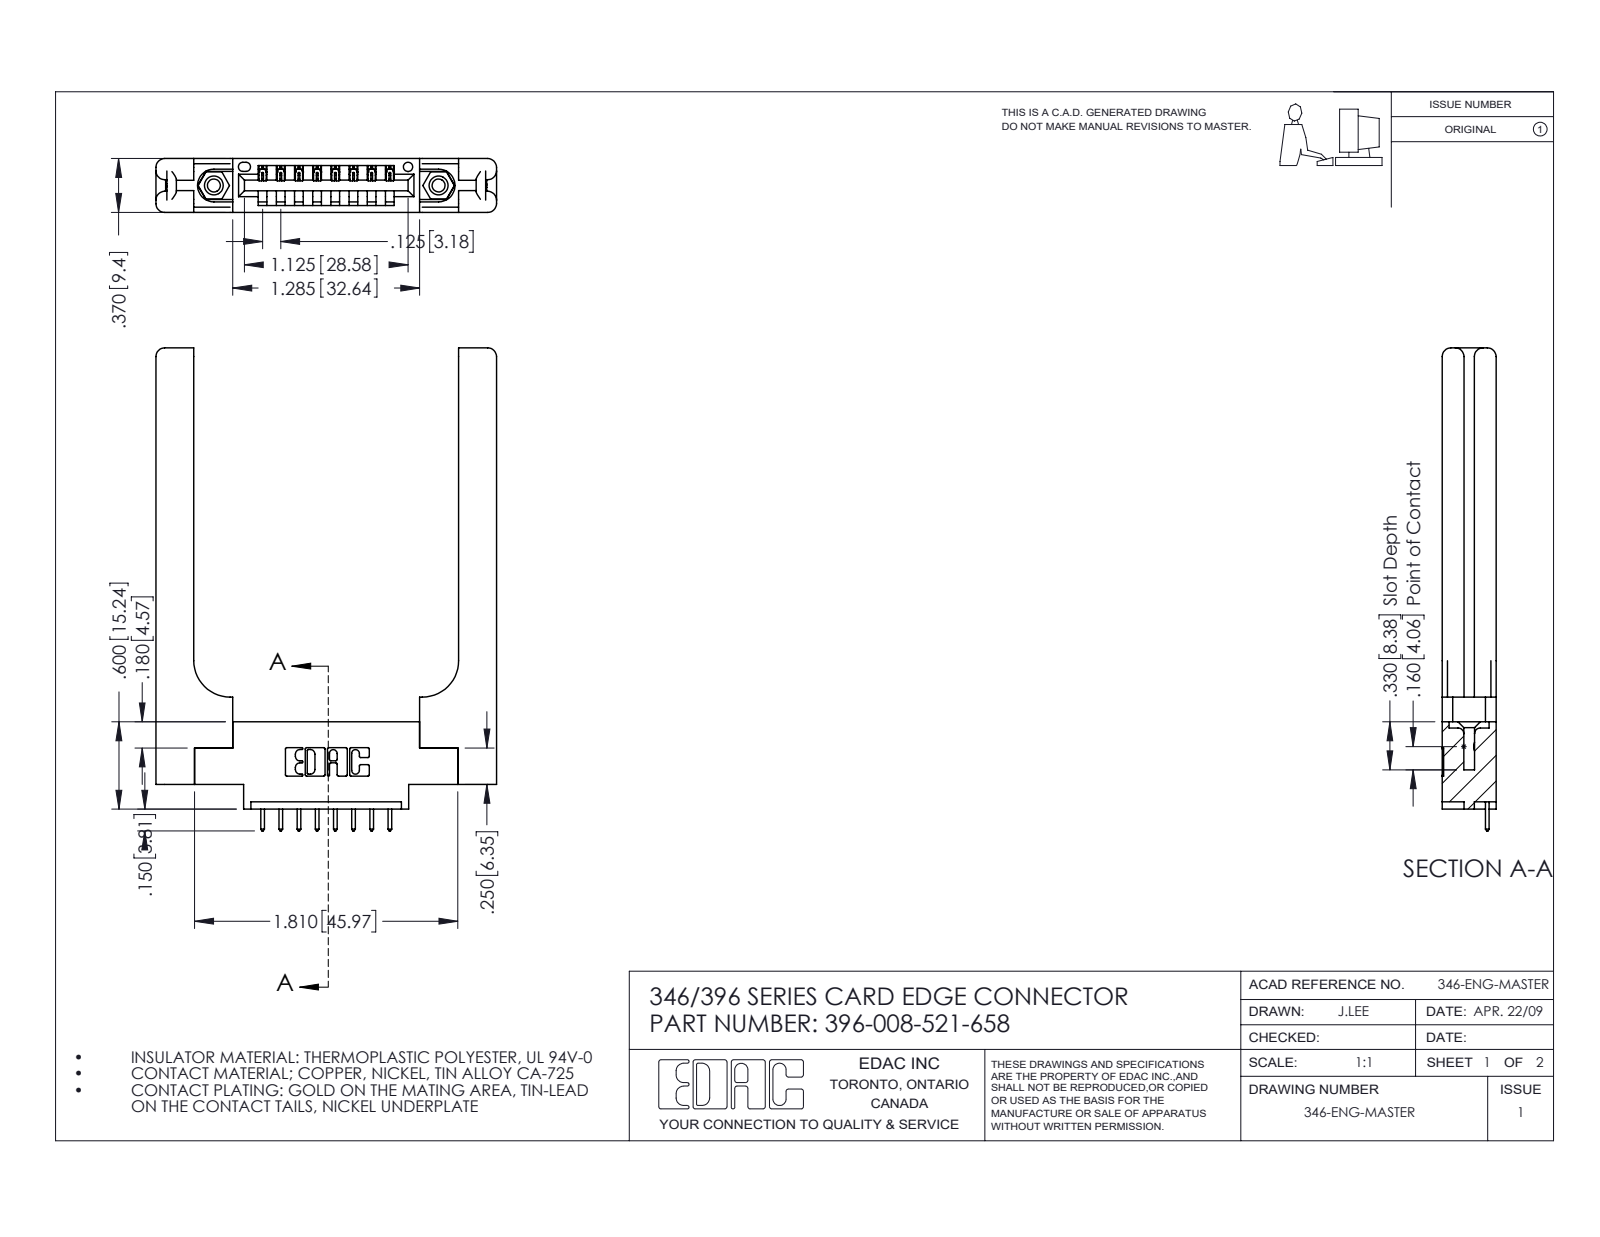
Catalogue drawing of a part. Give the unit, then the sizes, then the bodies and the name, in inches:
Units: inches
Overall size (bounding box): 3.32 × 2.341 × 0.37
Round holes (diameter × count): ⌀0.089 ×2, ⌀0.125 ×2, ⌀0.156 ×2, ⌀0.064 ×1
Round bosses / shafts (diameter × count): ⌀0.155 ×2
Partial cylindrical surfaces — rounded edges, fillets, slot ends (radius × count): R0.01 ×22, R0.006 ×16, R0.01 ×16, R0.06 ×16, R0.007 ×6, R0.031 ×6, R0.026 ×3, R0.03 ×2
Main face-to-face distances: 0.37, 0.15, 0.22, 0.072, 0.148, 0.25, 0.102, 0.048, 0.322, 0.173
Hole centre spacings: 0.246, 1.341, 1.545
Volume: 0.781 in³ · Surface area: 17.78 in²
Bodies: 13 solids, 846 faces (548 planar, 238 cylindrical, 60 other)
Part name (STEP PRODUCT): 345-292-001_345-293-121; 345-250-001_345-250-001-102; 396-008-521-658; 346-220-058_345-220-058 (+1 more)
STEP written by: SolidWorks 2016 (CONFIG_CONTROL_DESIGN)
